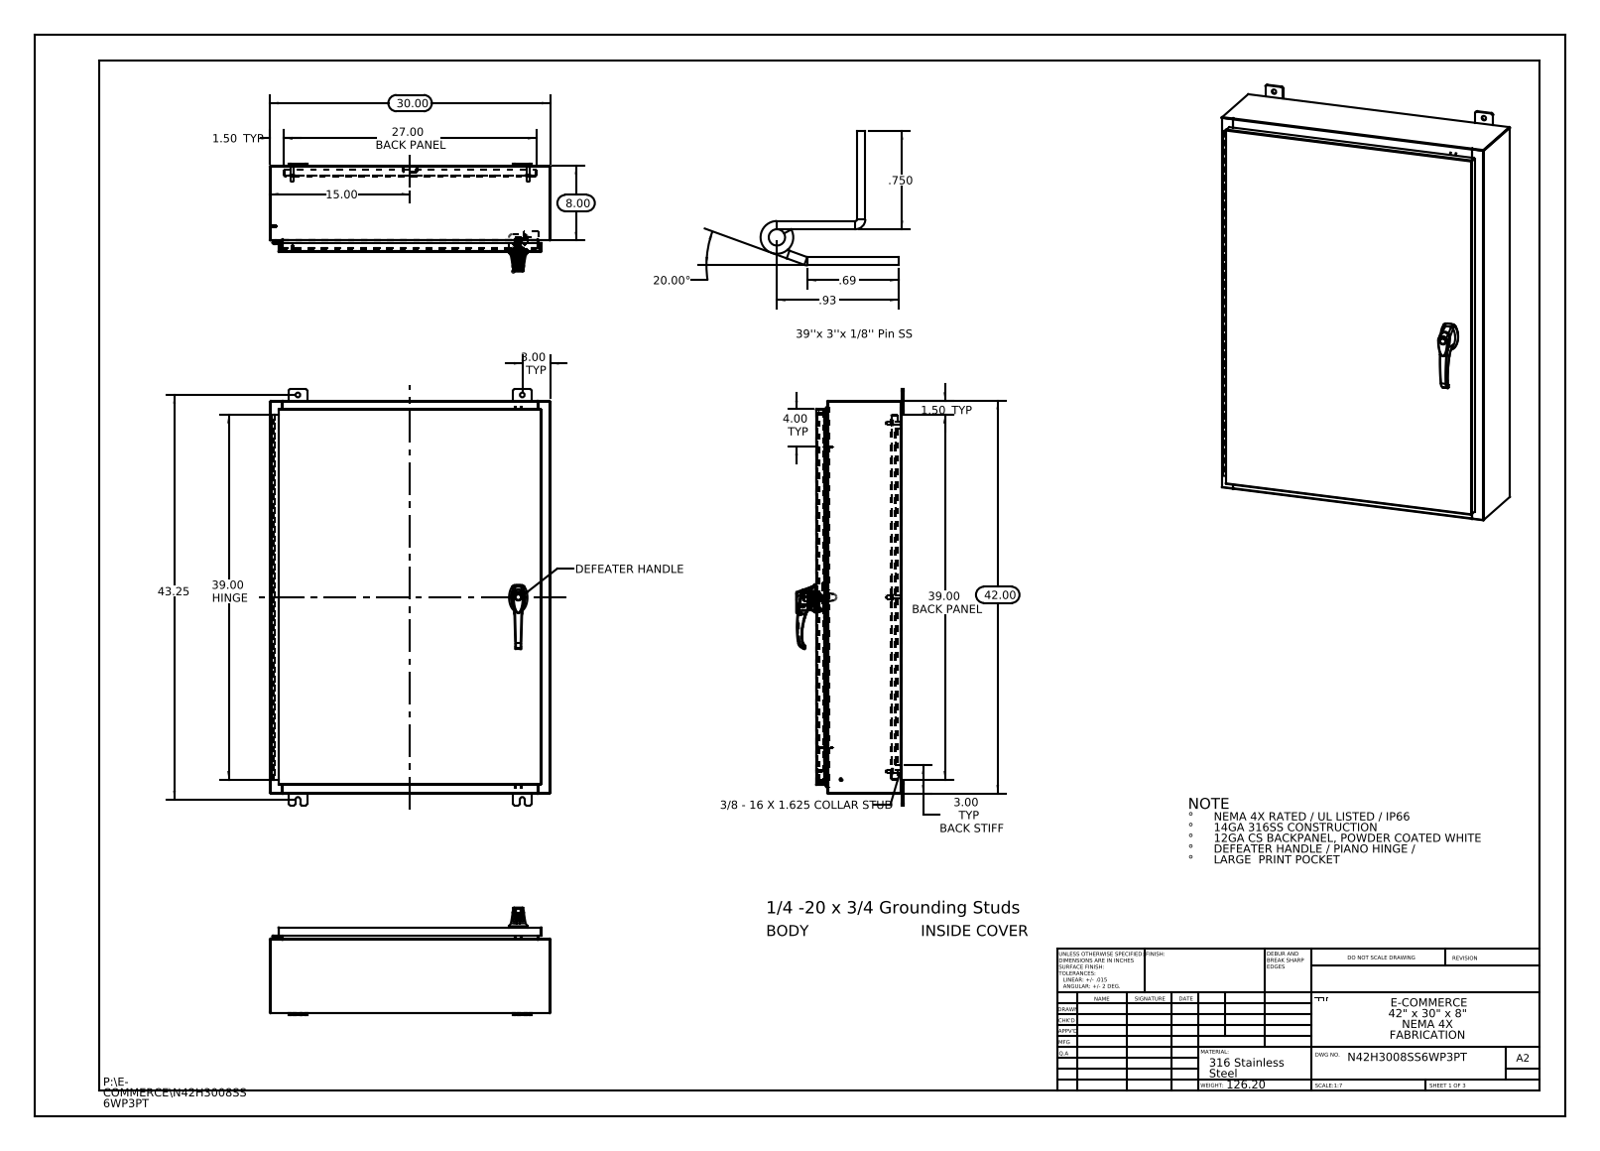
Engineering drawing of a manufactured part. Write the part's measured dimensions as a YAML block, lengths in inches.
part_name: "N42H3008SS6WP3PT 263033_Industrilas; N42H3008SS6WP3PT Body; N42H3008SS6WP3PT Enclosure Stiffener; 00005090 (+8 more)"
step_written_by: "SolidWorks 2013 (CONFIG_CONTROL_DESIGN)"
units: inches
bodies: {solids: 40, faces: 3038, planar: 1155, cylindrical: 1165, other: 718}
overall_size: [44.5, 30, 11.495]
volume: 446.2
surface_area: 11005
round_holes:
  - {diameter: 0.5, count: 10}
  - {diameter: 0.25, count: 4}
  - {diameter: 0.138, count: 3}
  - {diameter: 0.161, count: 3}
  - {diameter: 0.079, count: 2}
  - {diameter: 0.203, count: 2}
  - {diameter: 0.313, count: 2}
  - {diameter: 0.437, count: 2}
  - {diameter: 0.125, count: 1}
  - {diameter: 0.125, count: 1}
  - {diameter: 0.197, count: 1}
  - {diameter: 0.276, count: 1}
round_bosses_or_shafts:
  - {diameter: 0.625, count: 6}
  - {diameter: 0.375, count: 6}
  - {diameter: 0.33, count: 6}
  - {diameter: 0.157, count: 4}
  - {diameter: 0.14, count: 4}
  - {diameter: 0.315, count: 3}
  - {diameter: 0.236, count: 3}
  - {diameter: 1.181, count: 1}
partial_cylinders:
  - {radius: 0.118, count: 37}
  - {radius: 0.006, count: 33}
  - {radius: 0.013, count: 28}
  - {radius: 0.19, count: 24}
  - {radius: 0.088, count: 22}
  - {radius: 0.039, count: 15}
  - {radius: 0.028, count: 12}
  - {radius: 0.008, count: 6}
face_to_face_distances: [0.075, 9.126, 9.051, 0.104, 9.201, 1, 8.126, 1.075, 8.051, 1.179]
hole_center_spacings: [14.36, 16.667, 18.625, 31.376, 25.25, 0.295, 0.625, 0.841]
